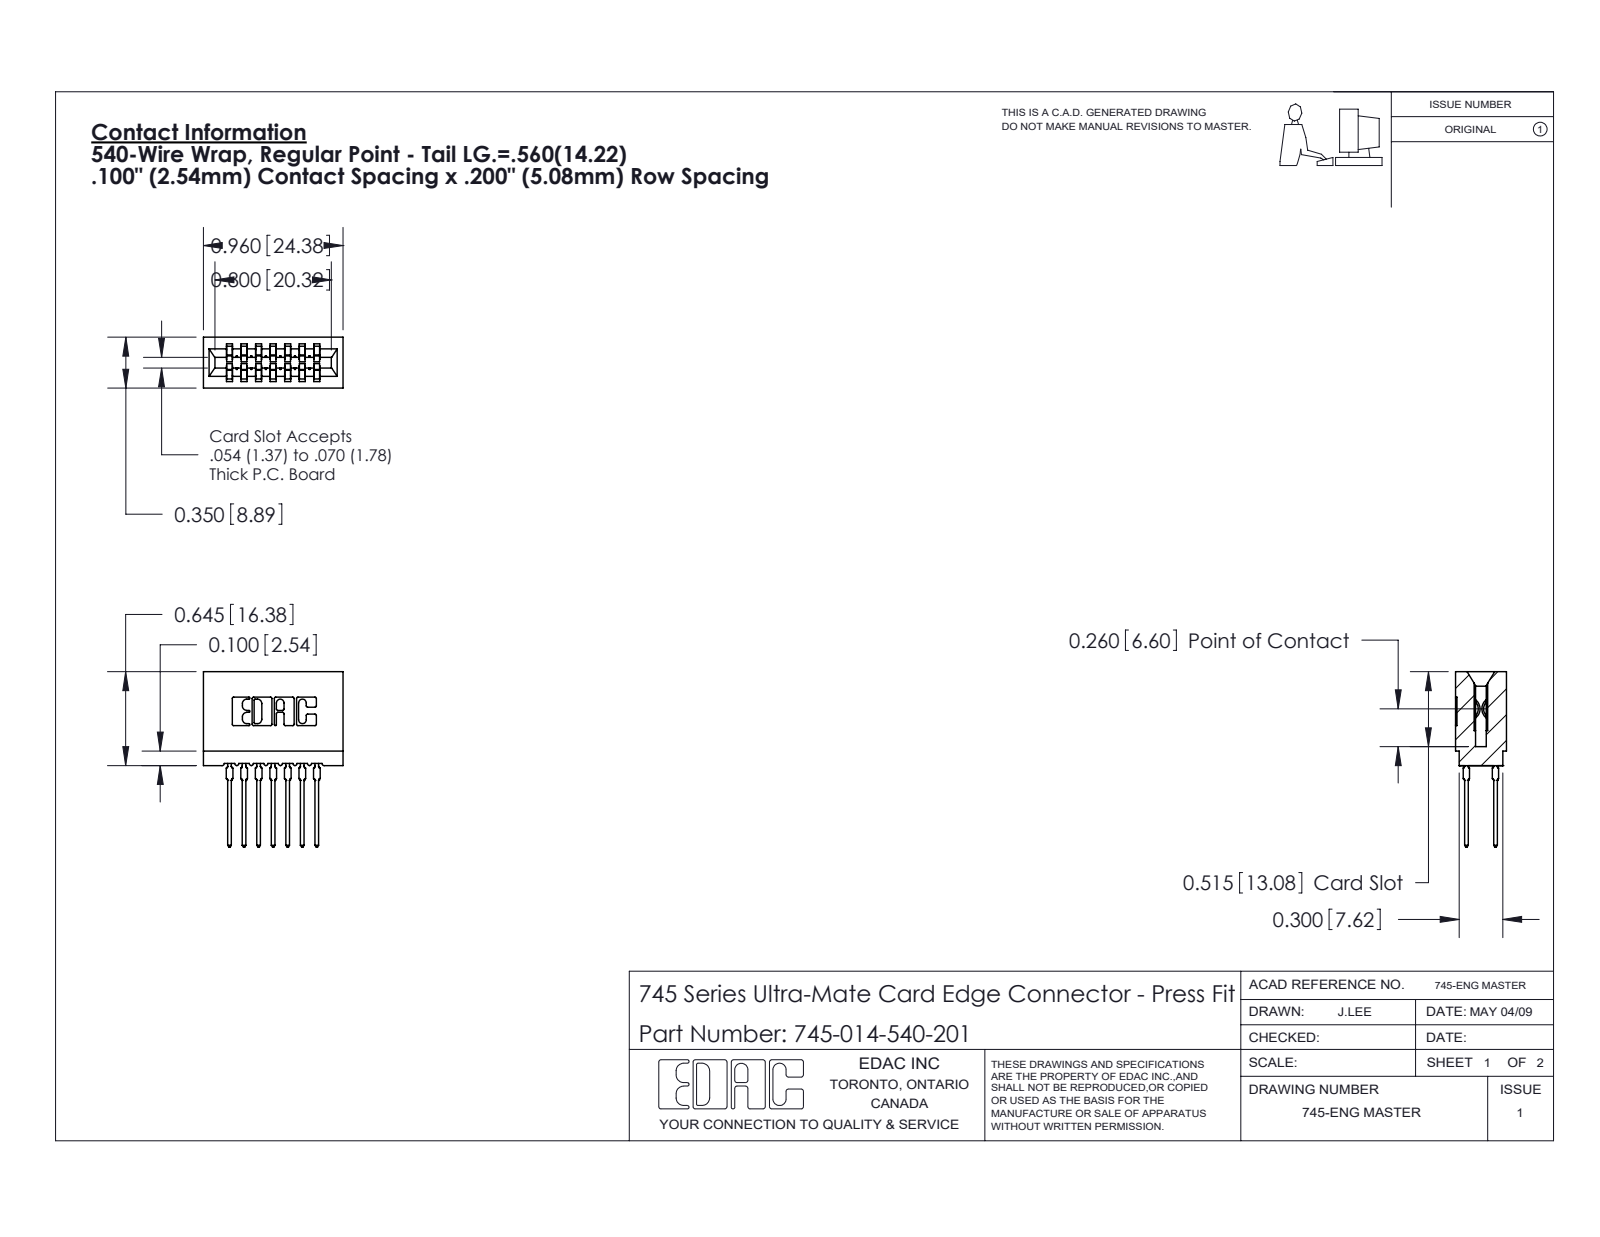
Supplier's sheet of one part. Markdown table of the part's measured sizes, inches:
| quantity | value |
| --- | --- |
| part name | 745-292-001_540; 745 Part_Insulator Option - 01; 745-014-540-201 |
| STEP written by | SolidWorks 2020 (CONFIG_CONTROL_DESIGN) |
| units | inches |
| bodies | 15 solids, 1348 faces (699 planar, 285 cylindrical, 364 other) |
| overall size | 1.206 × 0.96 × 0.35 |
| volume | 0.149 in³ |
| surface area | 6.711 in² |
| partial cylindrical surfaces (radius × count) | 0.021 × 28, 0.01 × 22, 0.015 × 14, 0.005 × 8, 0.011 × 8, 0.007 × 6, 0.031 × 6, 0.026 × 3 |
| main face-to-face distances | 0.1, 0.2, 0.3, 0.042, 0.142, 0.4, 0.058, 0.242, 0.158, 0.35 |
